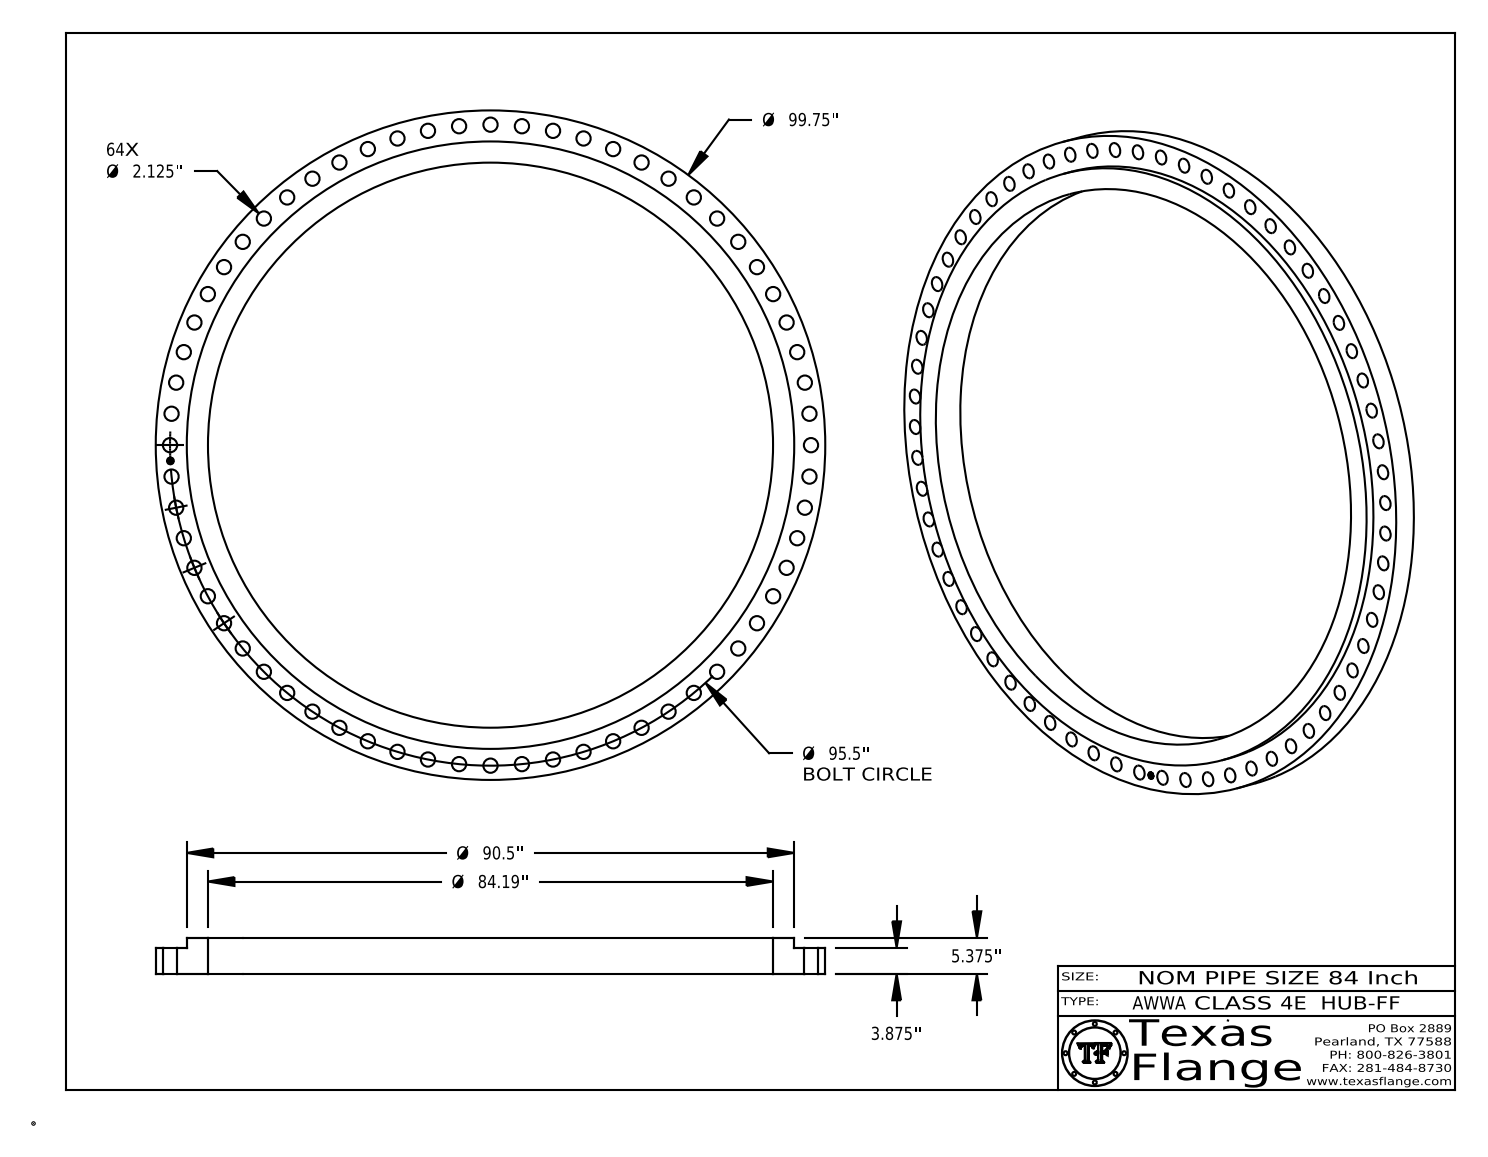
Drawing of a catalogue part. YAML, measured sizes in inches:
part_name: "AWWA Class 4E-HUB-FF"
step_written_by: "CATIA V5 STEP AP214 (AUTOMOTIVE_DESIGN)"
units: inches
bodies: {solids: 1, faces: 522, planar: 368, cylindrical: 154, other: 0}
overall_size: [99.75, 99.75, 5.375]
volume: 9130
surface_area: 8760
round_holes:
  - {diameter: 2.125, count: 64}
  - {diameter: 1, count: 1}
  - {diameter: 84.19, count: 1}
round_bosses_or_shafts:
  - {diameter: 0.061, count: 8}
  - {diameter: 99.75, count: 1}
  - {diameter: 90.5, count: 1}
  - {diameter: 0.788, count: 1}
face_to_face_distances: [3.875, 5.375, 1.5, 3.86, 0.015, 1.515, 0.298, 0.293, 0.055, 0.193]
hole_center_spacings: [9.361, 47.75, 4.686, 18.631, 23.205, 45.019, 36.546, 40.831]
